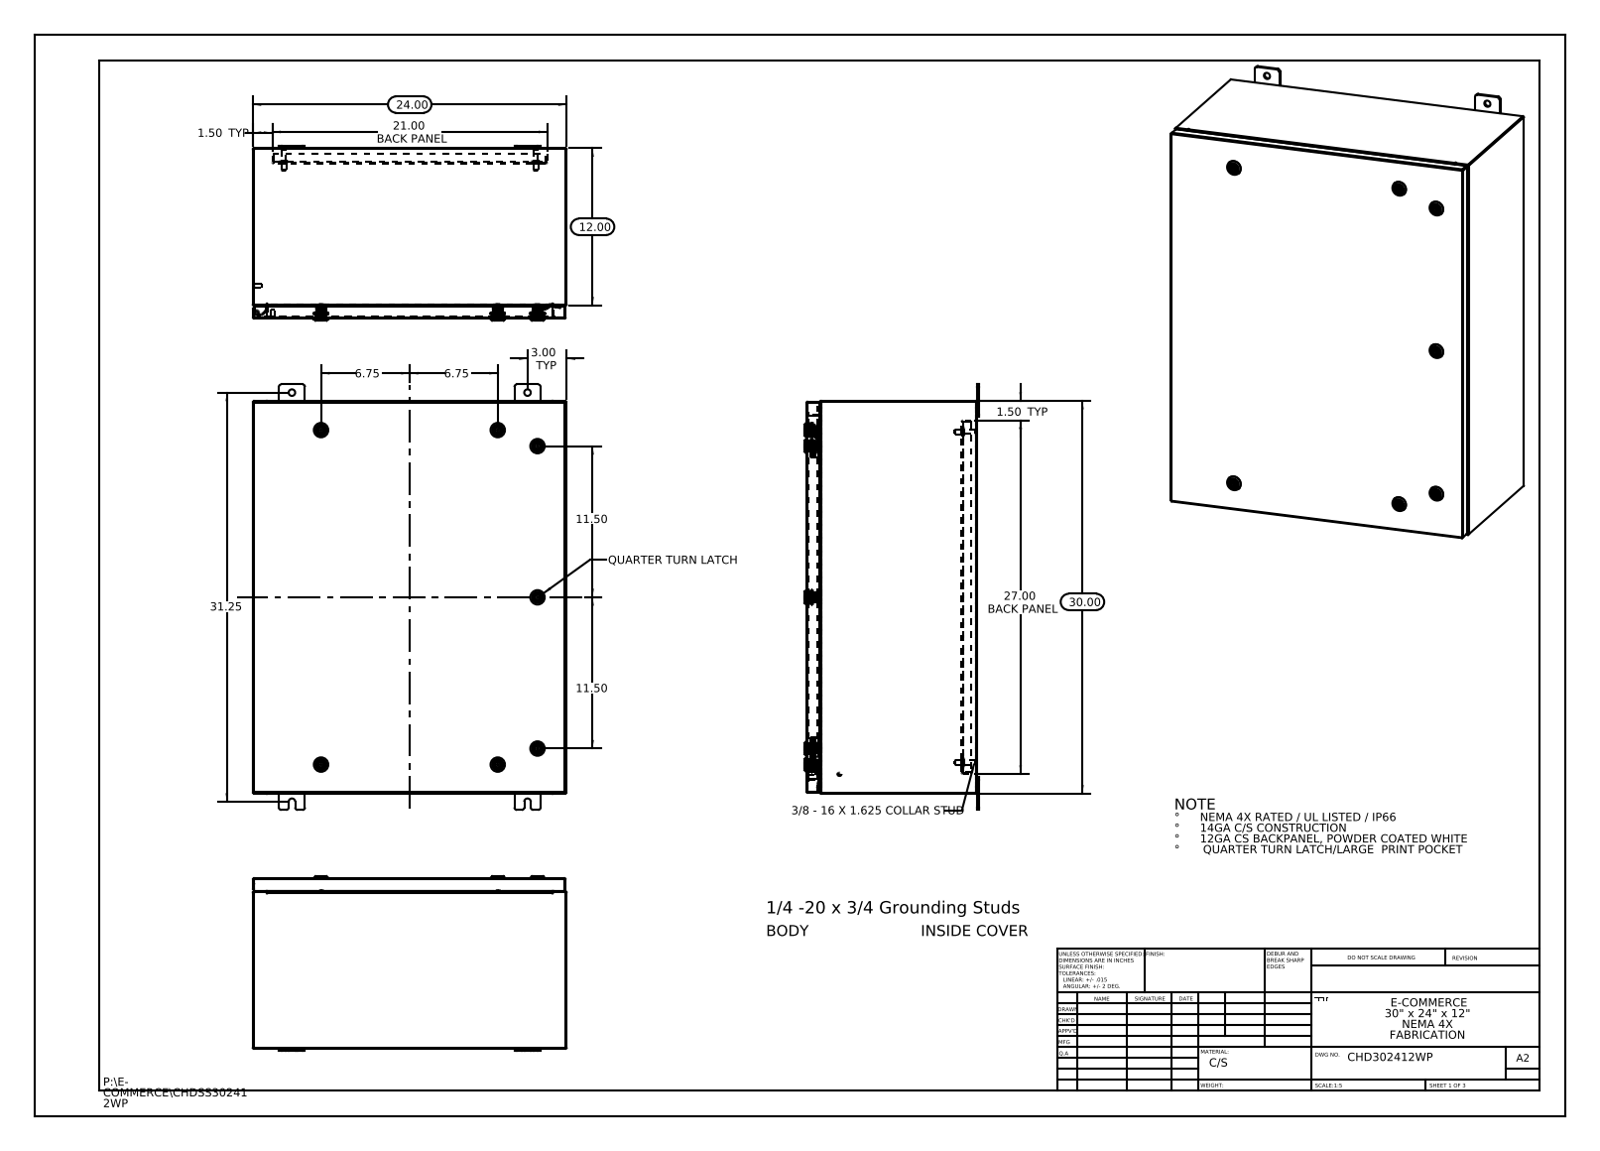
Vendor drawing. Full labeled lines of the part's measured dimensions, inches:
Part name (STEP PRODUCT): Washer-221320-IB-Industrilas_Washer-221320-IB-Industrilas; CHDSS302412WP Top; Housing-211301-IB-Industrilas_Housing-211301-IB-Industrilas; Concealed Hinge (Cover Side) (+8 more)
STEP written by: SolidWorks 2013 (CONFIG_CONTROL_DESIGN)
Units: inches
Bodies: 61 solids, 6252 faces (1822 planar, 1948 cylindrical, 2482 other)
Overall size (bounding box): 32.5 × 24 × 13.356
Volume: 299.1 in³ · Surface area: 7 484 in²
Round holes (diameter × count): ⌀0.5 ×8, ⌀0.197 ×7, ⌀0.394 ×7, ⌀0.4 ×7, ⌀0.63 ×7, ⌀0.787 ×7, ⌀0.136 ×4, ⌀0.211 ×1
Round bosses / shafts (diameter × count): ⌀0.236 ×9, ⌀1.102 ×7, ⌀0.78 ×7, ⌀0.626 ×7, ⌀0.61 ×7, ⌀0.531 ×7, ⌀0.392 ×7, ⌀0.114 ×7
Partial cylindrical surfaces — rounded edges, fillets, slot ends (radius × count): R0.006 ×231, R0.118 ×231, R0.028 ×84, R0.02 ×28, R0.197 ×28, R0.19 ×24, R0.013 ×22, R0.088 ×18
Main face-to-face distances: 0.075, 0.074, 23.925, 13.01, 12.935, 12.936, 12.861, 0.104, 1, 29.925
Hole centre spacings: 0.688, 1.858, 3.276, 11.55, 13.5, 16.583, 18, 19.25
